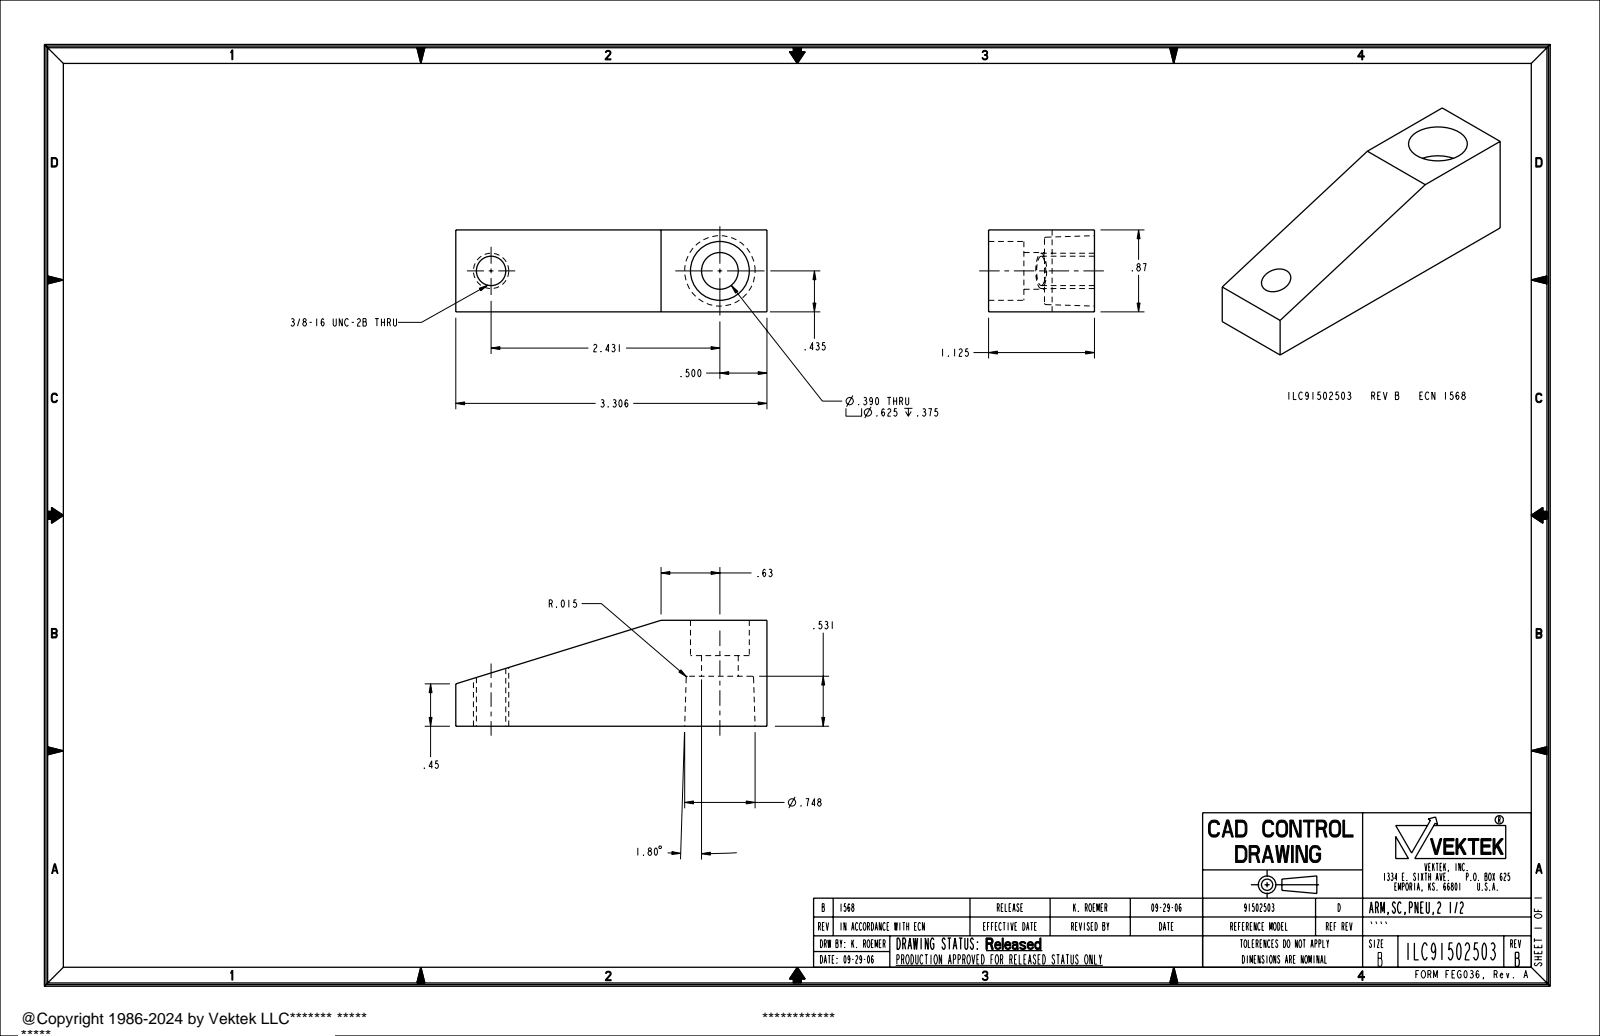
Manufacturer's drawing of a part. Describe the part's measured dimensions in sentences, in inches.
The part is named "ILC91502503". Its 3-D file was written by "PRO/ENGINEER BY PARAMETRIC TECHNOLOGY CORPORATION, 2005180 (AUTOMOTIVE_DESIGN_CC2)". It is 1 solid with 21 faces: 9 planar, 8 cylindrical and 4 other. Overall it measures 3.306 by 1.125 by 0.87 inches. Its volume is 2.188 cubic inches and its surface area 16.18 square inches. Round holes: 1 of diameter 0.312, 1 of diameter 0.39, 1 of diameter 0.625. Round bosses or shafts: 1 of diameter 0.375. The main face-to-face distances are 0.87, 1.125, 3.306, 0.531, 0.594, 0.75, 0.219, 0.375. The hole center spacings are 2.431.
